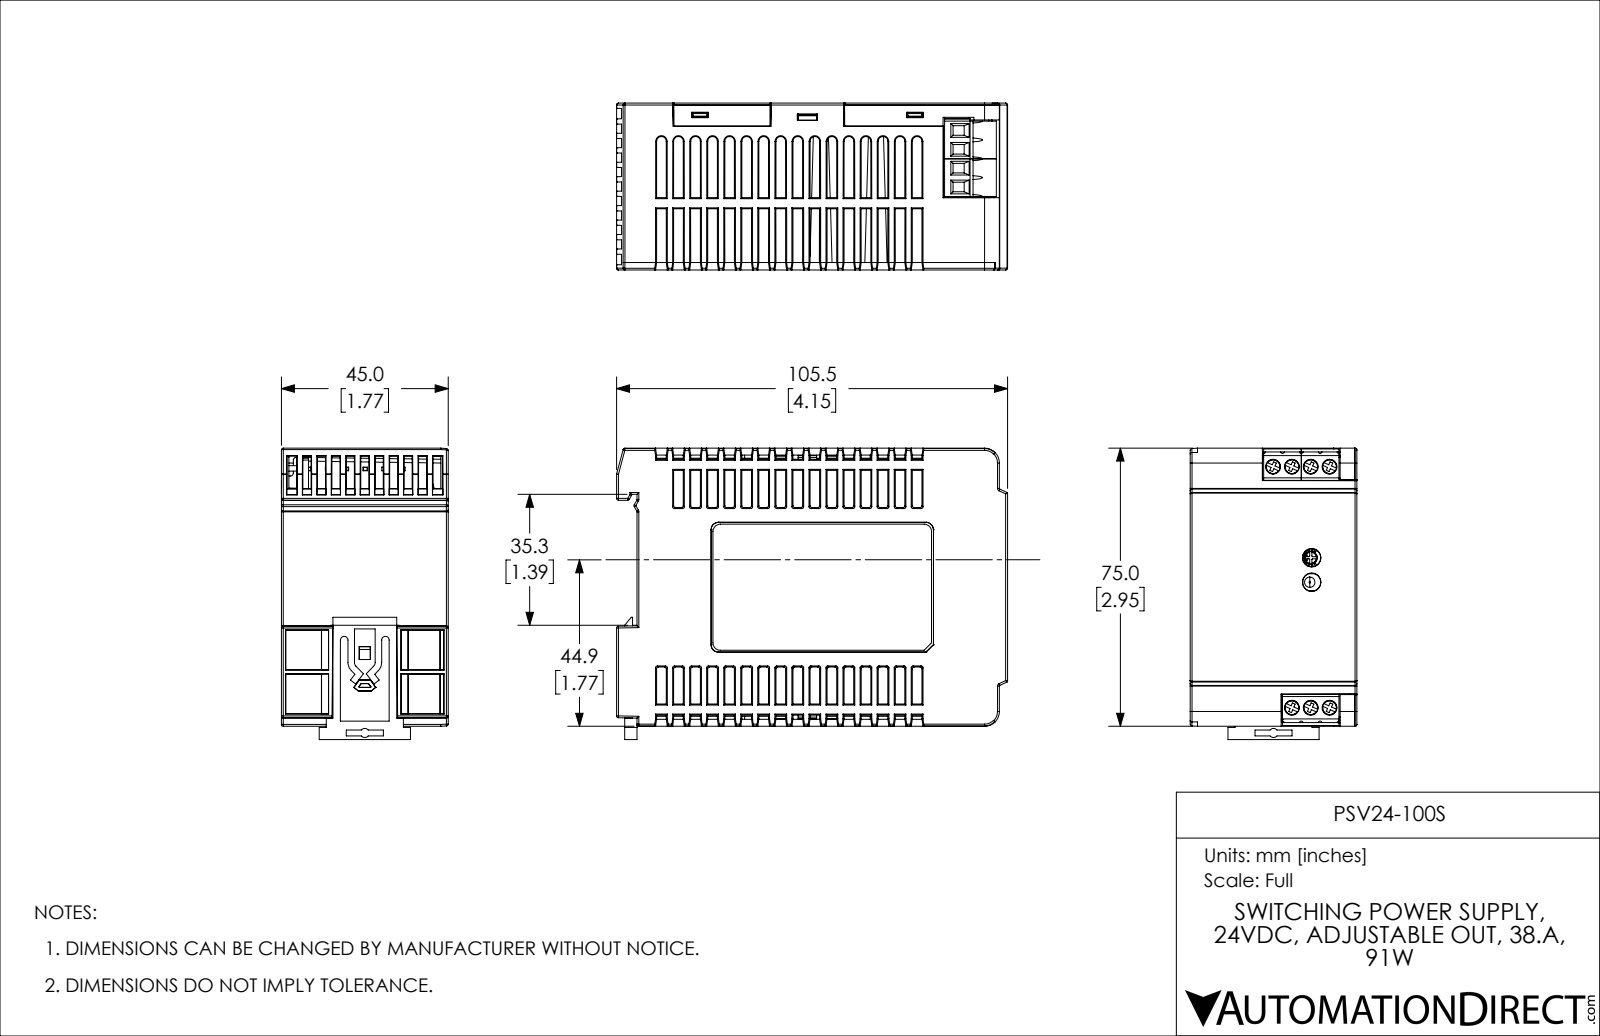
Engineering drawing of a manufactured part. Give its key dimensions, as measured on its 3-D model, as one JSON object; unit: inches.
{"part_name": "PSV24-100S", "step_written_by": "SolidWorks 2017 (AUTOMOTIVE_DESIGN)", "units": "inches", "bodies": {"solids": 12, "faces": 2809, "planar": 2200, "cylindrical": 337, "other": 272}, "overall_size": [4.154, 3.095, 1.772], "volume_in3": 4.29, "surface_area_in2": 149.5, "round_holes": [[0.029, 10], [0.036, 10], [0.157, 9], [0.158, 7], [0.023, 3], [0.028, 2], [0.079, 2], [0.138, 1]], "round_bosses_or_shafts": [[0.154, 7], [0.134, 1], [0.11, 1]], "partial_cylinders_radius": [[0.02, 117], [0.03, 16], [0.02, 9], [0.008, 8], [0.049, 7], [0.004, 6], [0.059, 5], [0.037, 4]], "face_to_face_distances": [0.063, 1.693, 0.079, 0.287, 0.224, 0.071, 0.146, 0.209, 1.476, 1.406], "hole_center_spacings": [0.1, 0.2, 0.3, 1.079, 1.179, 1.279, 0.4, 0.979]}
